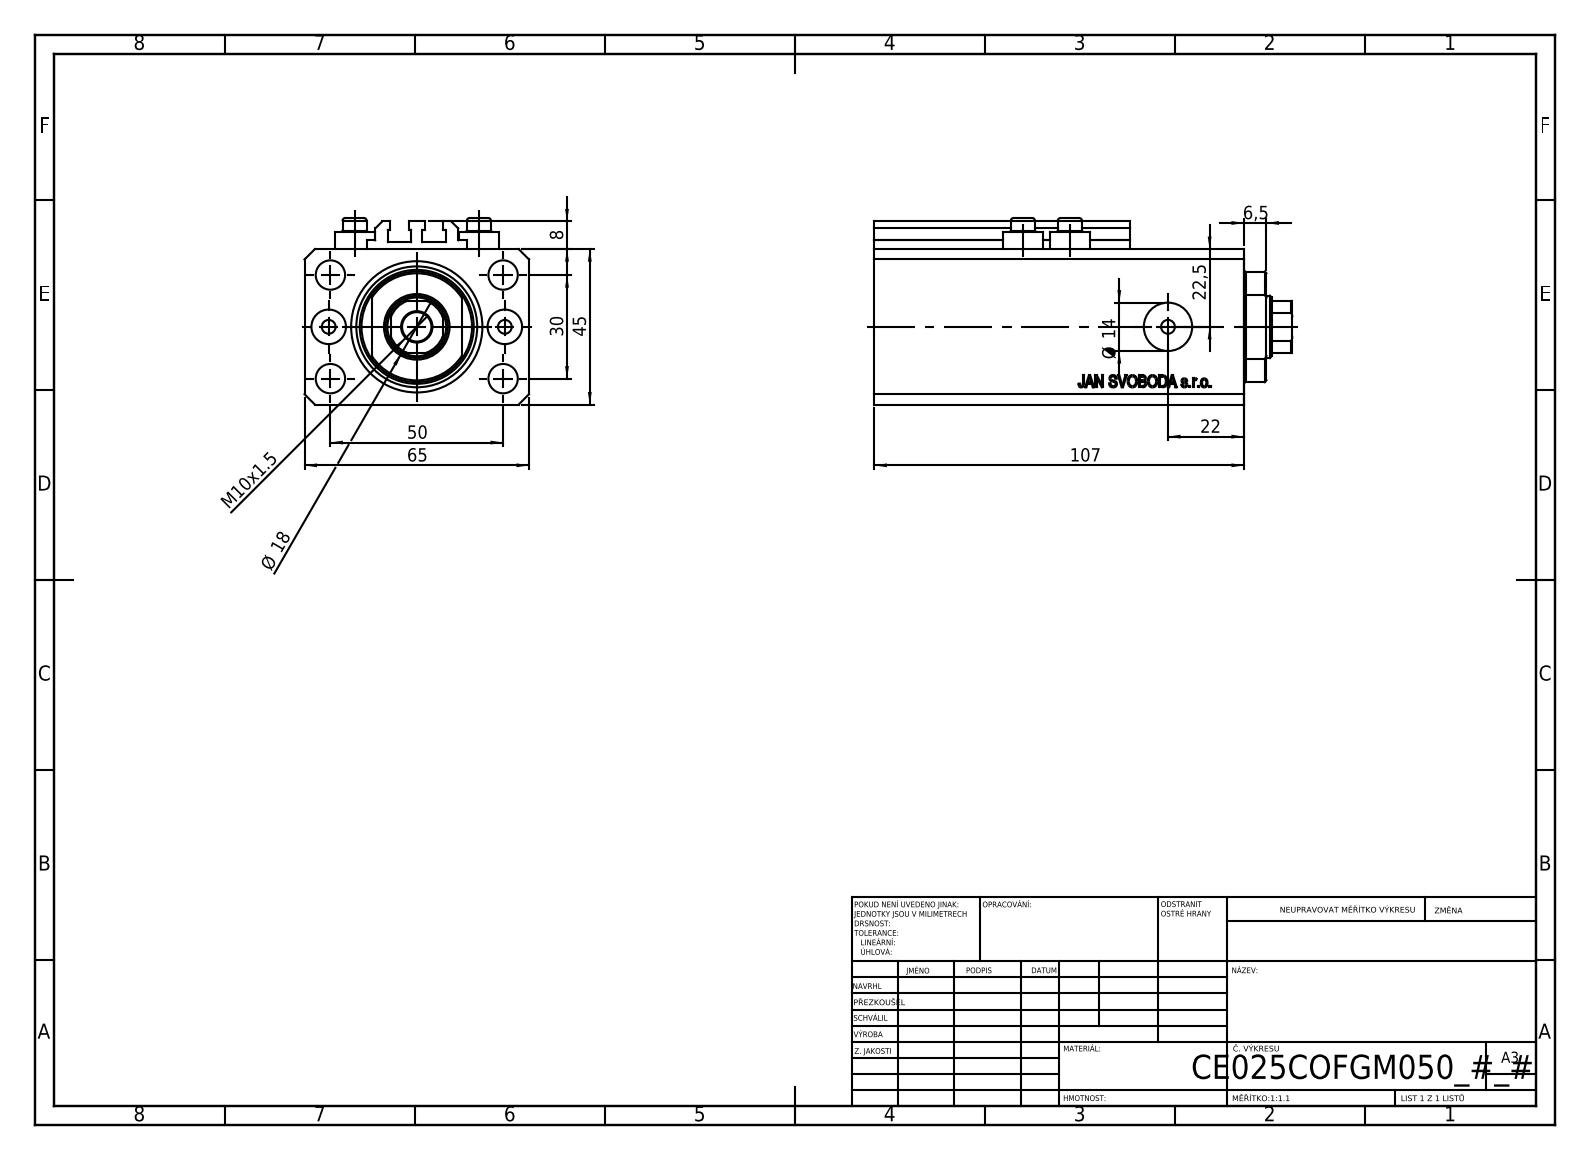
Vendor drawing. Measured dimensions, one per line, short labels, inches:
name: V250CE_VC_C; ALLEN BOLT V250CE; V250CE_C_VCP; V250CE_C_Body
written by: SolidWorks 2019 (CONFIG_CONTROL_DESIGN)
unit: in
bodies: 8 solids, 1034 faces (504 planar, 86 cylindrical, 444 other)
size: 4.764 × 2.559 × 2.126
volume: 17.64 in³; area: 114.6 in²
holes: 8× ⌀0.157, 5× ⌀0.335, 2× ⌀0.394, 2× ⌀0.551, 1× ⌀0.709, 1× ⌀0.984, 1× ⌀1.496
bosses: 4× ⌀0.457, 4× ⌀0.276
rounds: 10× R0.008, 1× R0.335, 1× R0.63
face distances: 1.772, 2.559, 0.551, 3.661, 4.213, 1.85, 0.098, 0.807, 0.394, 0.079
hole spacings: 0.591, 1.148, 2.074, 0.535, 1.004, 1.181, 1.417, 1.515
